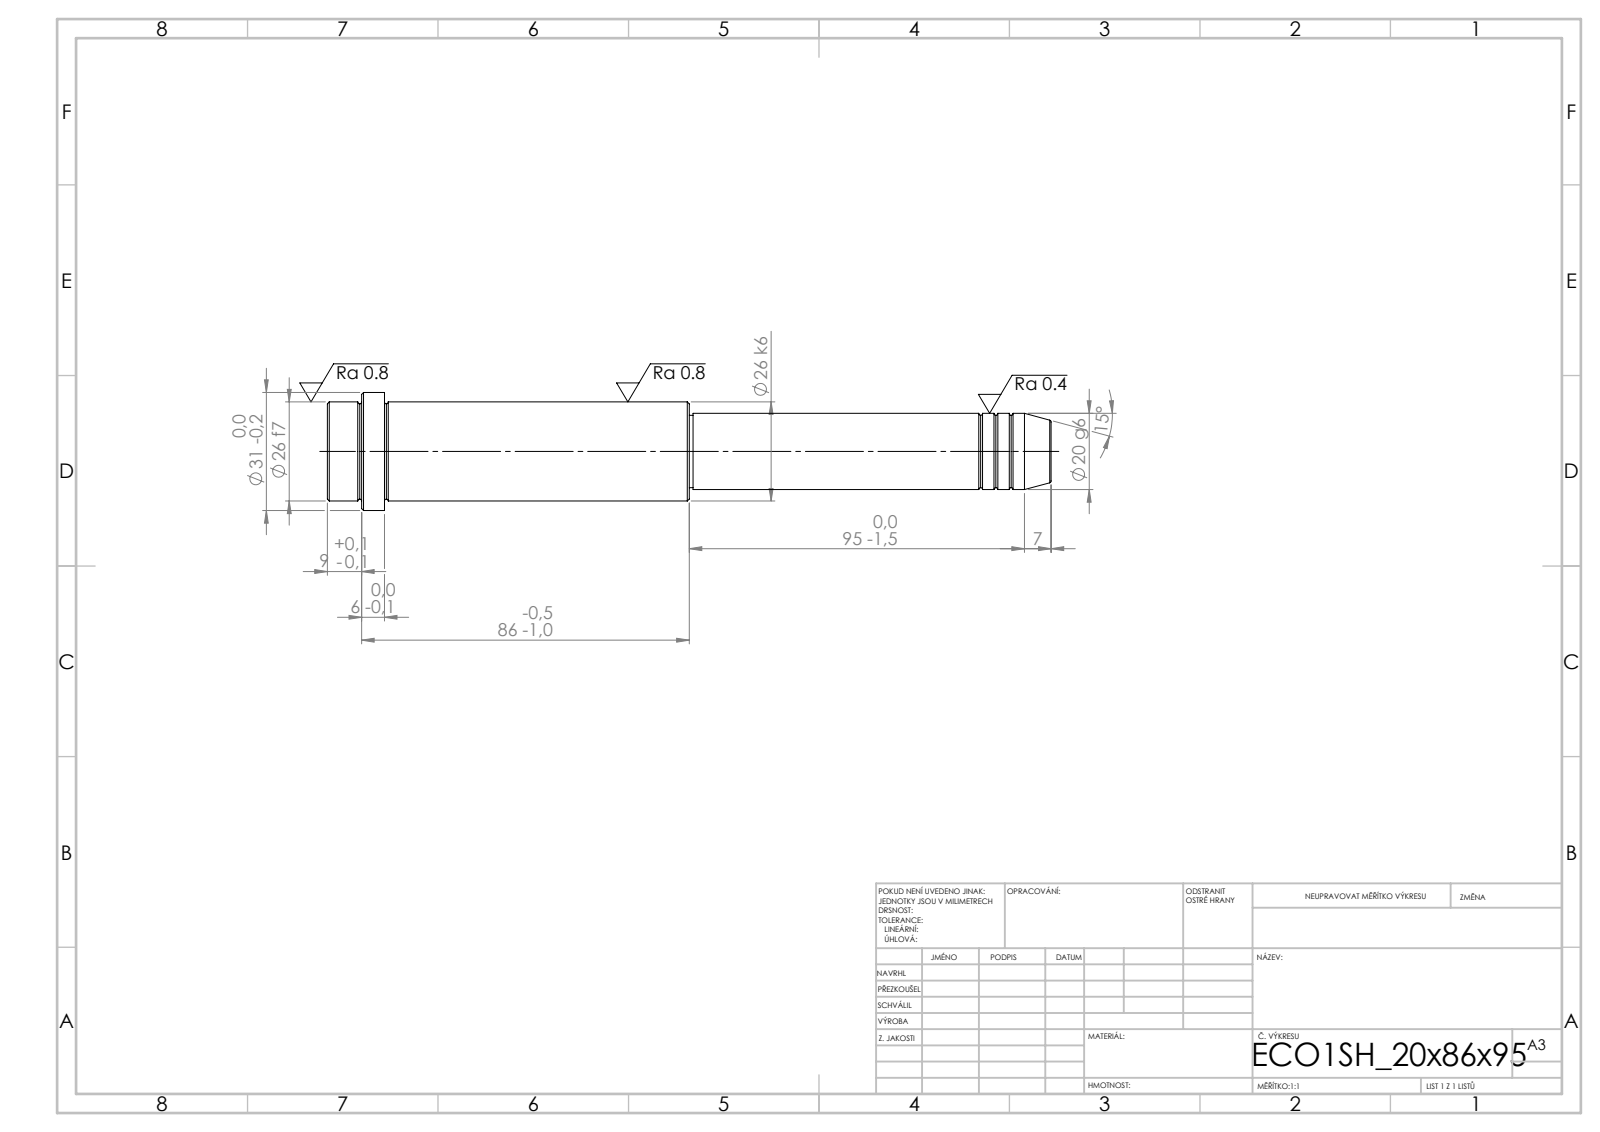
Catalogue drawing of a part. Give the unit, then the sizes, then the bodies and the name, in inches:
Units: inches
Overall size (bounding box): 7.48 × 1.22 × 1.22
Round bosses / shafts (diameter × count): ⌀1.22 ×1, ⌀1.024 ×1, ⌀0.787 ×1, ⌀0.748 ×1
Main face-to-face distances: 3.74, 0.591, 3.15, 6.89, 7.48, 7.126, 3.386, 0.236, 0.354, 3.701
Volume: 4.945 in³ · Surface area: 23.81 in²
Bodies: 1 solid, 52 faces (6 planar, 16 cylindrical, 30 other)
STEP written by: SolidWorks 2019 (CONFIG_CONTROL_DESIGN)
